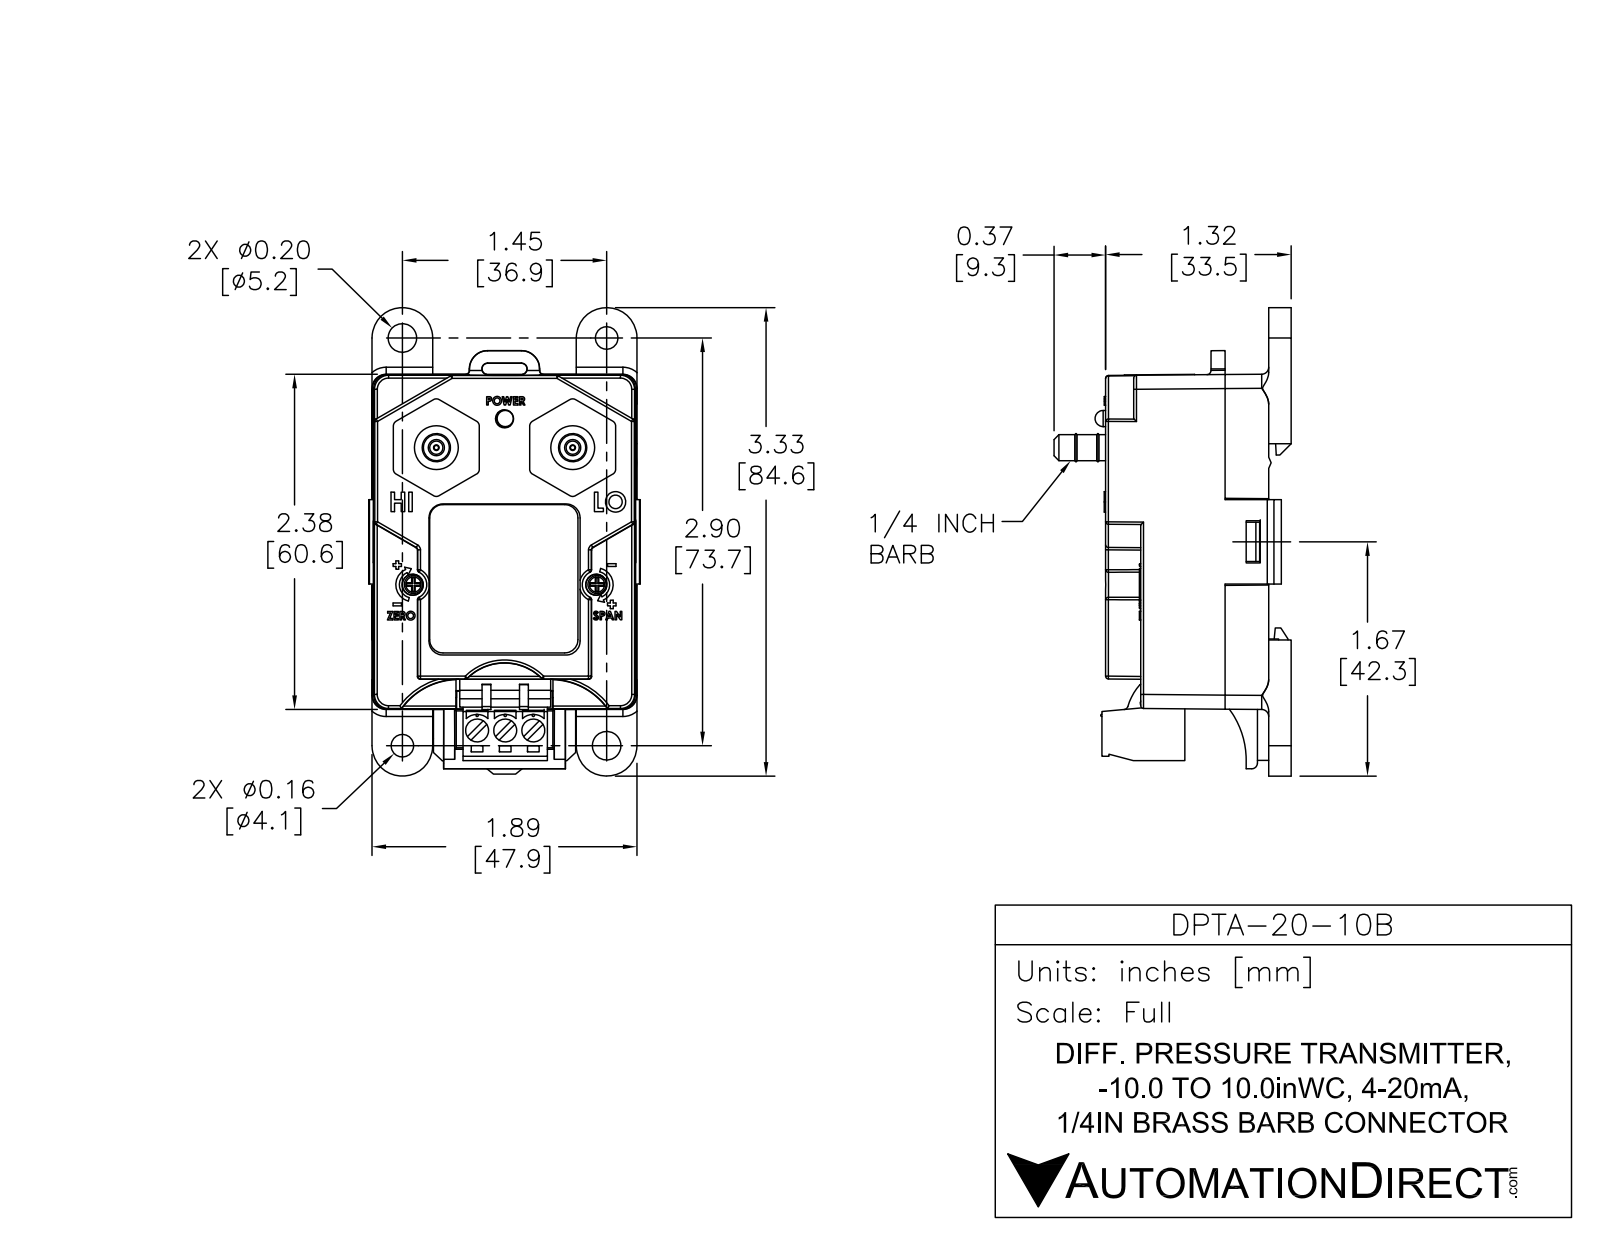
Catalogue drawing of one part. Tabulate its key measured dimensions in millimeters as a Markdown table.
| quantity | value |
| --- | --- |
| part name | DPTA-20-10B |
| STEP written by | SolidWorks 2011 (AUTOMOTIVE_DESIGN) |
| units | millimeters |
| bodies | 11 solids, 448 faces (354 planar, 85 cylindrical, 9 other) |
| overall size | 85.01 × 49.76 × 43.1 |
| volume | 29 684 mm³ |
| surface area | 34 743 mm² |
| round holes (diameter × count) | 4 × 7, 2.5 × 2, 5.12 × 2, 3.1 × 1 |
| round bosses / shafts (diameter × count) | 5 × 3, 3.5 × 3, 3.5 × 3, 8 × 2, 4.75 × 2, 3 × 1 |
| partial cylindrical surfaces (radius × count) | 3 × 12, 2 × 4, 5.5 × 4, 0.99 × 2, 1.06 × 2, 1.12 × 2, 2.38 × 2, 3.25 × 2 |
| main face-to-face distances | 1, 1.9, 4, 29.1, 0.5, 46.9, 5.9, 5, 33.1, 27.2 |
| hole center spacings | 13.55, 20.73, 23.37, 24.92, 29.43, 34.46, 36.67, 38.22 |
